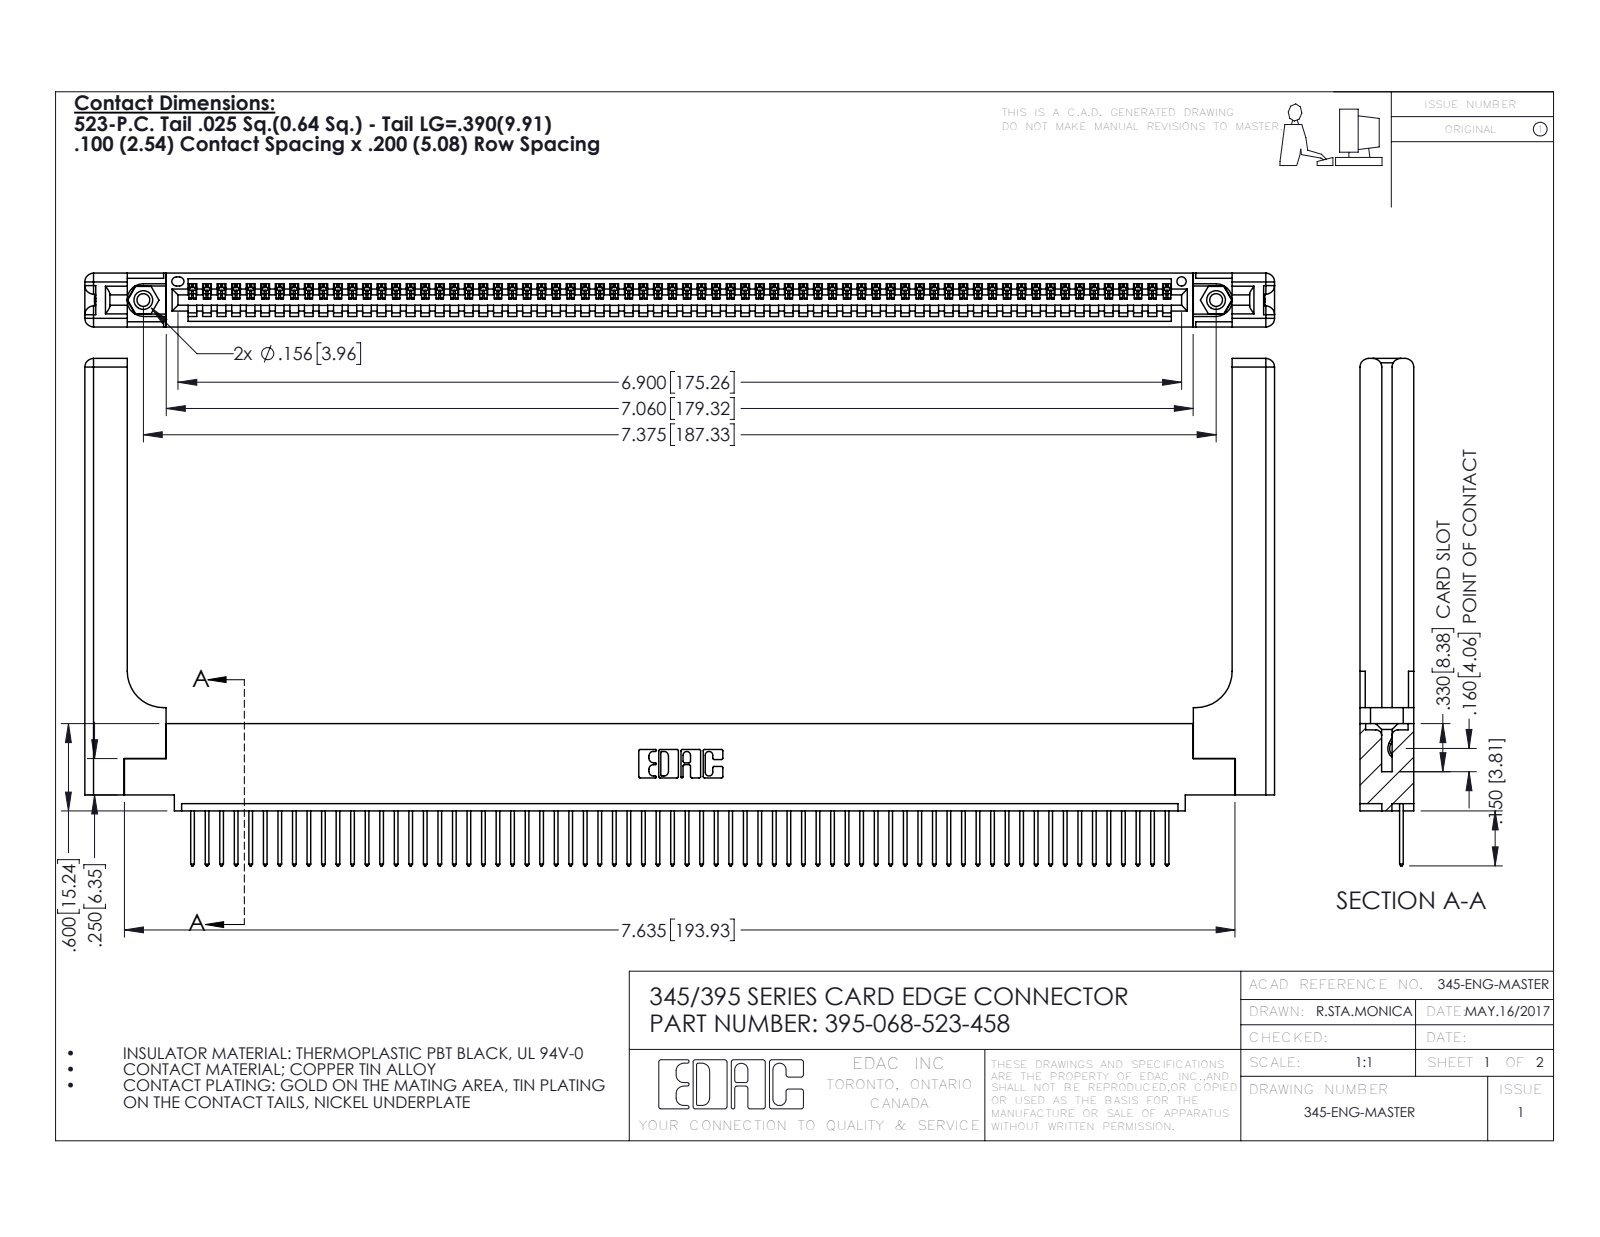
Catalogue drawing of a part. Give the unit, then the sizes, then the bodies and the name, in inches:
Units: inches
Overall size (bounding box): 8.179 × 3.487 × 0.37
Round holes (diameter × count): ⌀0.089 ×2, ⌀0.125 ×2, ⌀0.156 ×2, ⌀0.064 ×1
Round bosses / shafts (diameter × count): ⌀0.155 ×2
Partial cylindrical surfaces — rounded edges, fillets, slot ends (radius × count): R0.006 ×136, R0.01 ×136, R0.01 ×22, R0.06 ×16, R0.007 ×6, R0.031 ×6, R0.026 ×3, R0.03 ×2
Main face-to-face distances: 0.072, 0.298, 0.37, 0.098, 0.272, 0.025, 0.2, 0.225, 0.148, 0.15
Hole centre spacings: 0.27, 7.139, 7.375
Volume: 1.73 in³ · Surface area: 49.89 in²
Bodies: 73 solids, 4330 faces (2952 planar, 1318 cylindrical, 60 other)
Part name (STEP PRODUCT): 345 Part_0.110 Offset - 0.156 Dia-TH; 395-068-523-458; 345-250-001_345-250-001-102; 345-220-058_345-220-058 (+1 more)
STEP written by: SolidWorks 2016 (CONFIG_CONTROL_DESIGN)
